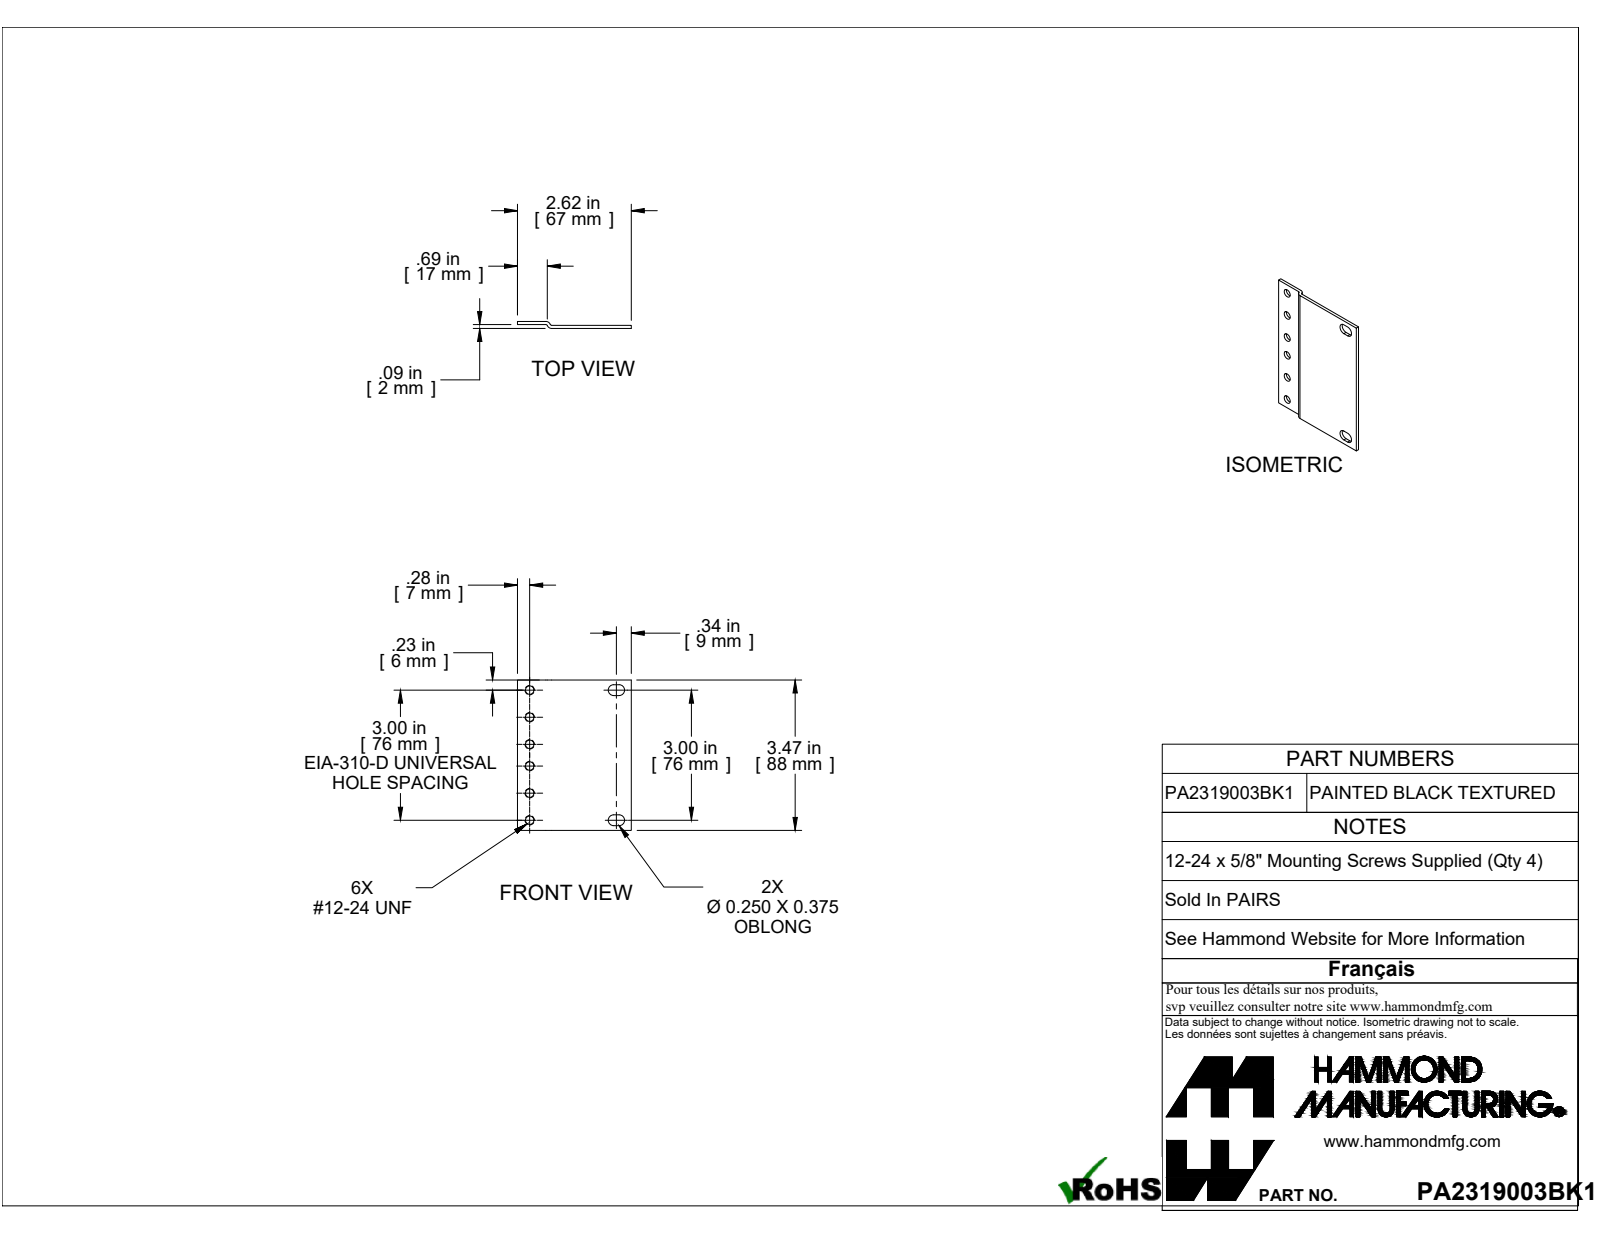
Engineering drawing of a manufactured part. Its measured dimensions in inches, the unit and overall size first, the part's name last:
Units: inches
Overall size (bounding box): 3.468 × 2.625 × 0.162
Round holes (diameter × count): ⌀0.159 ×6
Partial cylindrical surfaces — rounded edges, fillets, slot ends (radius × count): R0.125 ×4, R0.036 ×2, R0.108 ×2
Main face-to-face distances: 0.072, 0.09, 0.162, 0.018, 0.09, 0.072, 2.625, 3.468, 0.109, 0.359
Hole centre spacings: 0.625, 0.625, 1.125, 1.25, 1.75, 2.375, 0.5, 1.75
Volume: 0.645 in³ · Surface area: 19.15 in²
Bodies: 1 solid, 26 faces (12 planar, 14 cylindrical, 0 other)
Part name (STEP PRODUCT): PA2319003BK1
STEP written by: SolidWorks 2019 (AUTOMOTIVE_DESIGN)
